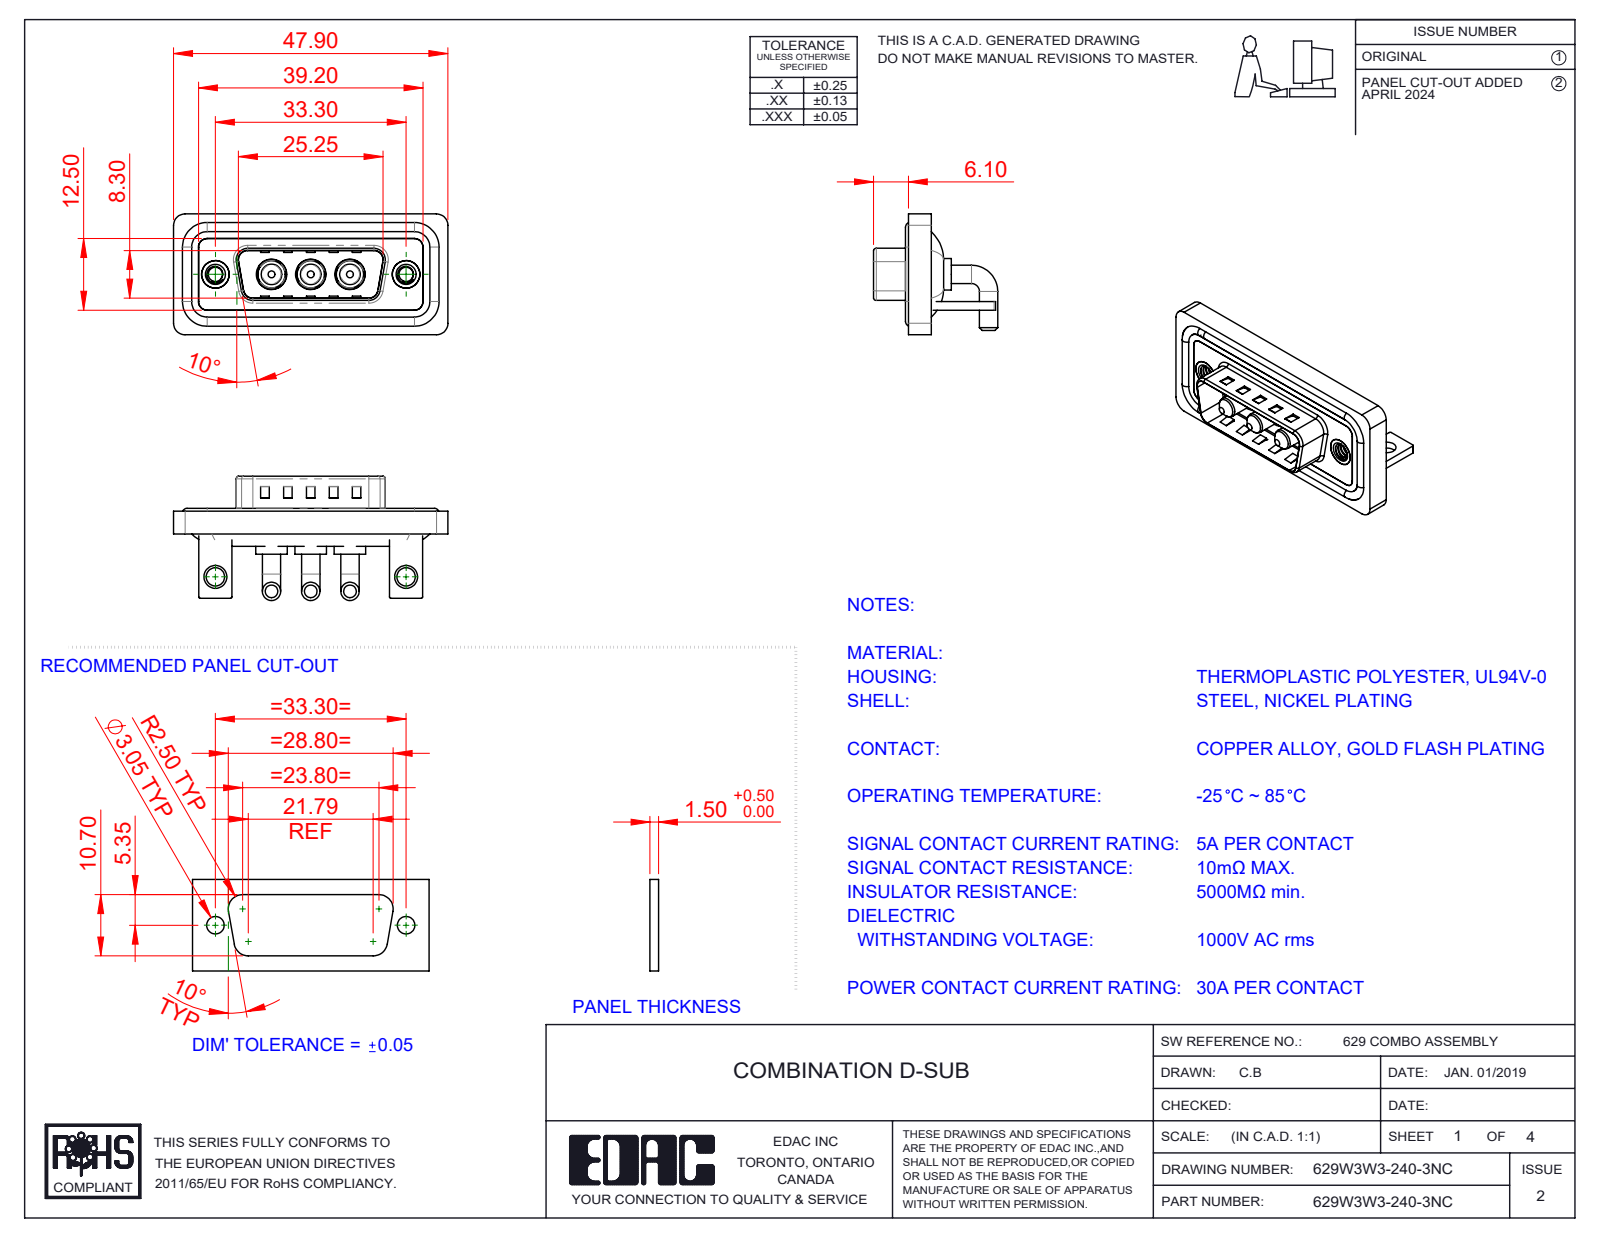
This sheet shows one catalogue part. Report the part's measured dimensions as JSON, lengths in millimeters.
{"part_name": "629Combo Housing_3W3; Power Pin_30A RA; 629W3W3-240-3NC; 629Combo Shell Front_15 Contacts (+4 more)", "step_written_by": "SolidWorks 2023 (CONFIG_CONTROL_DESIGN)", "units": "millimeters", "bodies": {"solids": 15, "faces": 614, "planar": 227, "cylindrical": 265, "other": 122}, "overall_size": [47.9, 21.7, 21.1], "volume_mm3": 6134, "surface_area_mm2": 9680, "round_holes": [[4.85, 3], [5.3, 3], [2.5, 2], [3.2, 2], [4, 2], [4.8, 2], [5, 2]], "round_bosses_or_shafts": [[3.2, 6], [1.6, 4], [5.5, 3], [5.2, 3], [4.75, 3], [3.75, 3], [3.6, 3], [4.9, 2]], "partial_cylinders_radius": [[2, 21], [1.5, 18], [0.25, 16], [0.5, 9], [1.6, 8], [0.6, 4], [0.65, 4], [0.9, 4]], "face_to_face_distances": [0.4, 1.5, 0.8, 2.9, 1.1, 2.1, 3.7, 1.6, 1.2, 4.5], "hole_center_spacings": [6.85, 9.8, 16.65, 23.5, 33.3, 13.7]}
